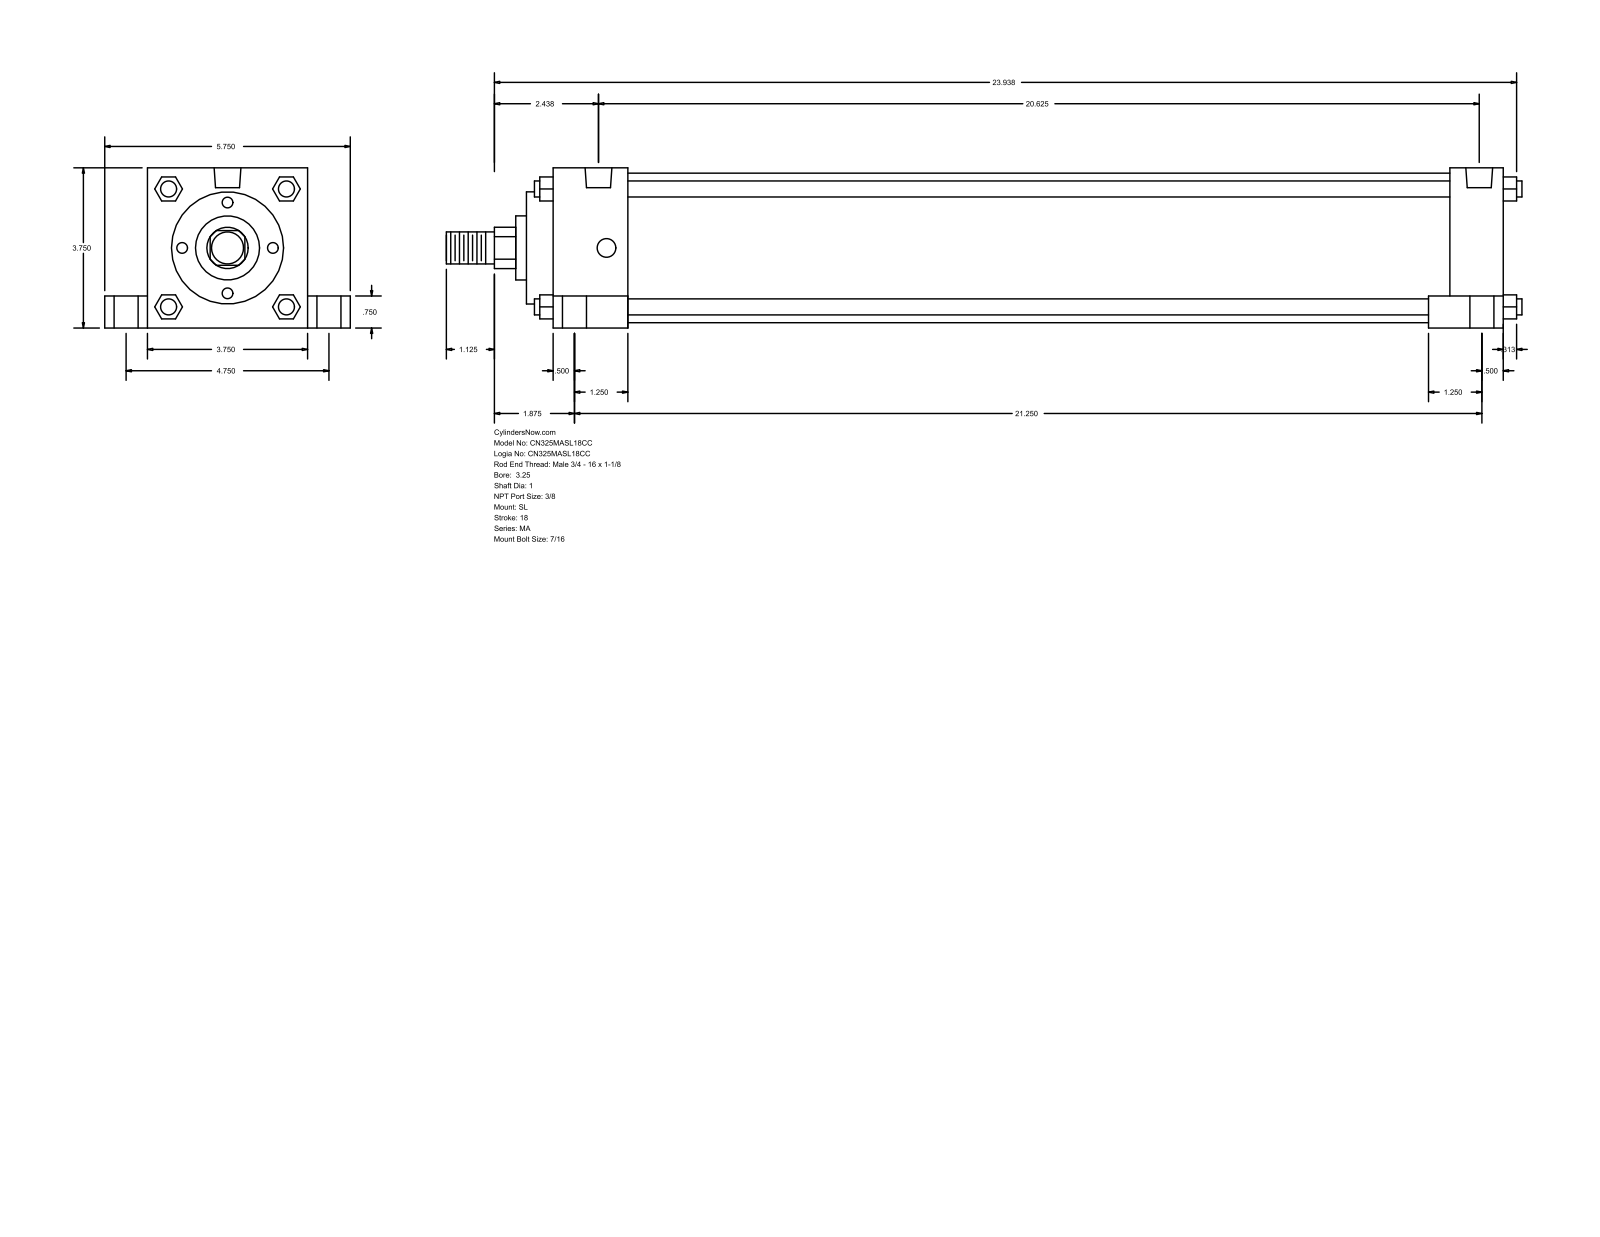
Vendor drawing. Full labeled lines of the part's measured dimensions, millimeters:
Part name (STEP PRODUCT): MA_SL__0325_1
STEP written by: GSSL Pune (CONFIG_CONTROL_DESIGN)
Units: millimetres
Bodies: 0 solids, 150 faces (113 planar, 37 cylindrical, 0 other)
Overall size (bounding box): 639.76 × 146.05 × 95.25
Round holes (diameter × count): ⌀11.11 ×4, ⌀14.29 ×4, ⌀20.64 ×4, ⌀15.93 ×2
Round bosses / shafts (diameter × count): ⌀9.53 ×4, ⌀88.9 ×1, ⌀66.67 ×1, ⌀38.1 ×1, ⌀25.4 ×1, ⌀19.05 ×1
Partial cylindrical surfaces — rounded edges, fillets, slot ends (radius × count): R12.29 ×1
Main face-to-face distances: 95.24, 565.16, 488.95, 15.87, 25.41, 120.65, 19.05, 533.41, 31.75, 44.46
Hole centre spacings: 60.35, 60.66, 62, 63.27, 120.66, 514.35, 524.19, 528.92
